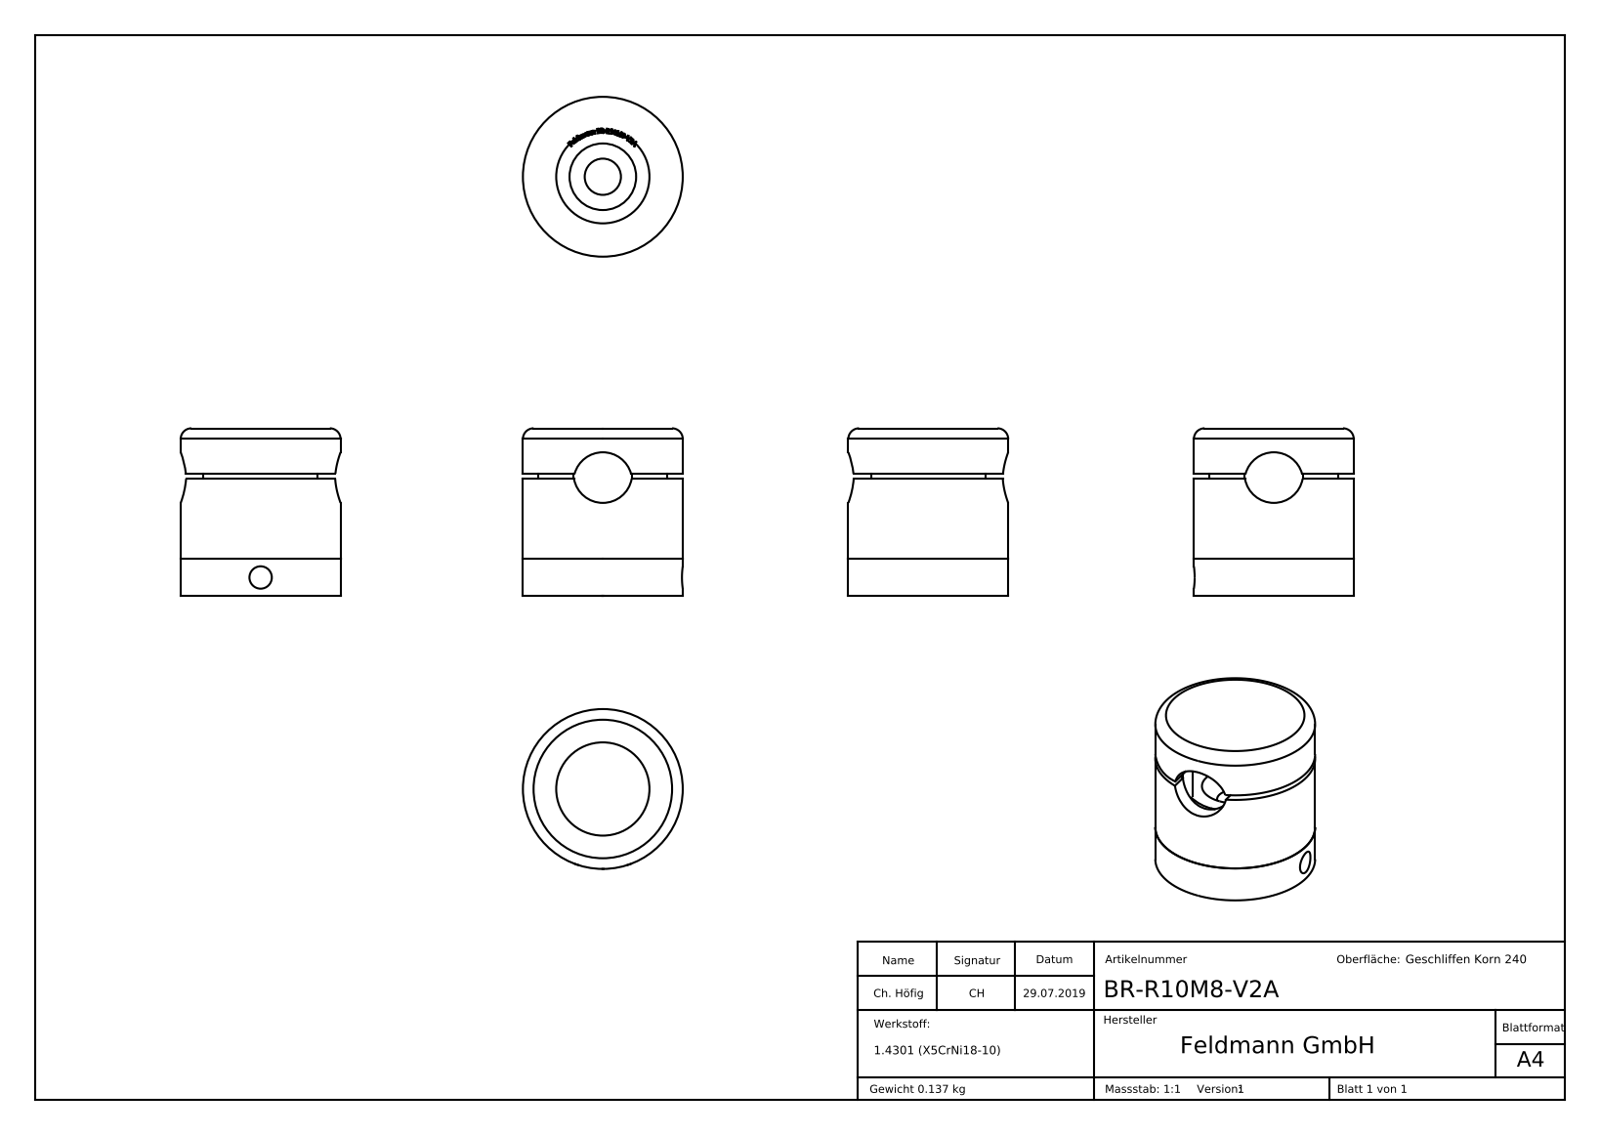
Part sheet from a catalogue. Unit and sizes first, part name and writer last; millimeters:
Units: millimetres
Overall size (bounding box): 64.34 × 30 × 30
Round holes (diameter × count): ⌀4.2 ×1, ⌀6.8 ×1, ⌀12.5 ×1, ⌀24.2 ×1
Round bosses / shafts (diameter × count): ⌀30 ×1, ⌀20 ×1
Partial cylindrical surfaces — rounded edges, fillets, slot ends (radius × count): R5.5 ×2, R8.75 ×1, R12.05 ×1
Main face-to-face distances: 7, 31.5, 24.5, 16, 8.5, 23, 15.5, 22, 15, 1
Volume: 17 288 mm³ · Surface area: 9 596 mm²
Bodies: 3 solids, 322 faces (185 planar, 15 cylindrical, 122 other)
Part name (STEP PRODUCT): BR-R1XM8-XXX Teil1_BR-1XM8-V2A Teil1; BR-R10M8-V2A; BR-R1XM8-XXX Teil2_BR-R10M8-V2A Teil2; BR-R1XM8-XXX Teil3_BR-R10M8-V2A Teil3 (+3 more)
STEP written by: SolidWorks 2015 (CONFIG_CONTROL_DESIGN)
